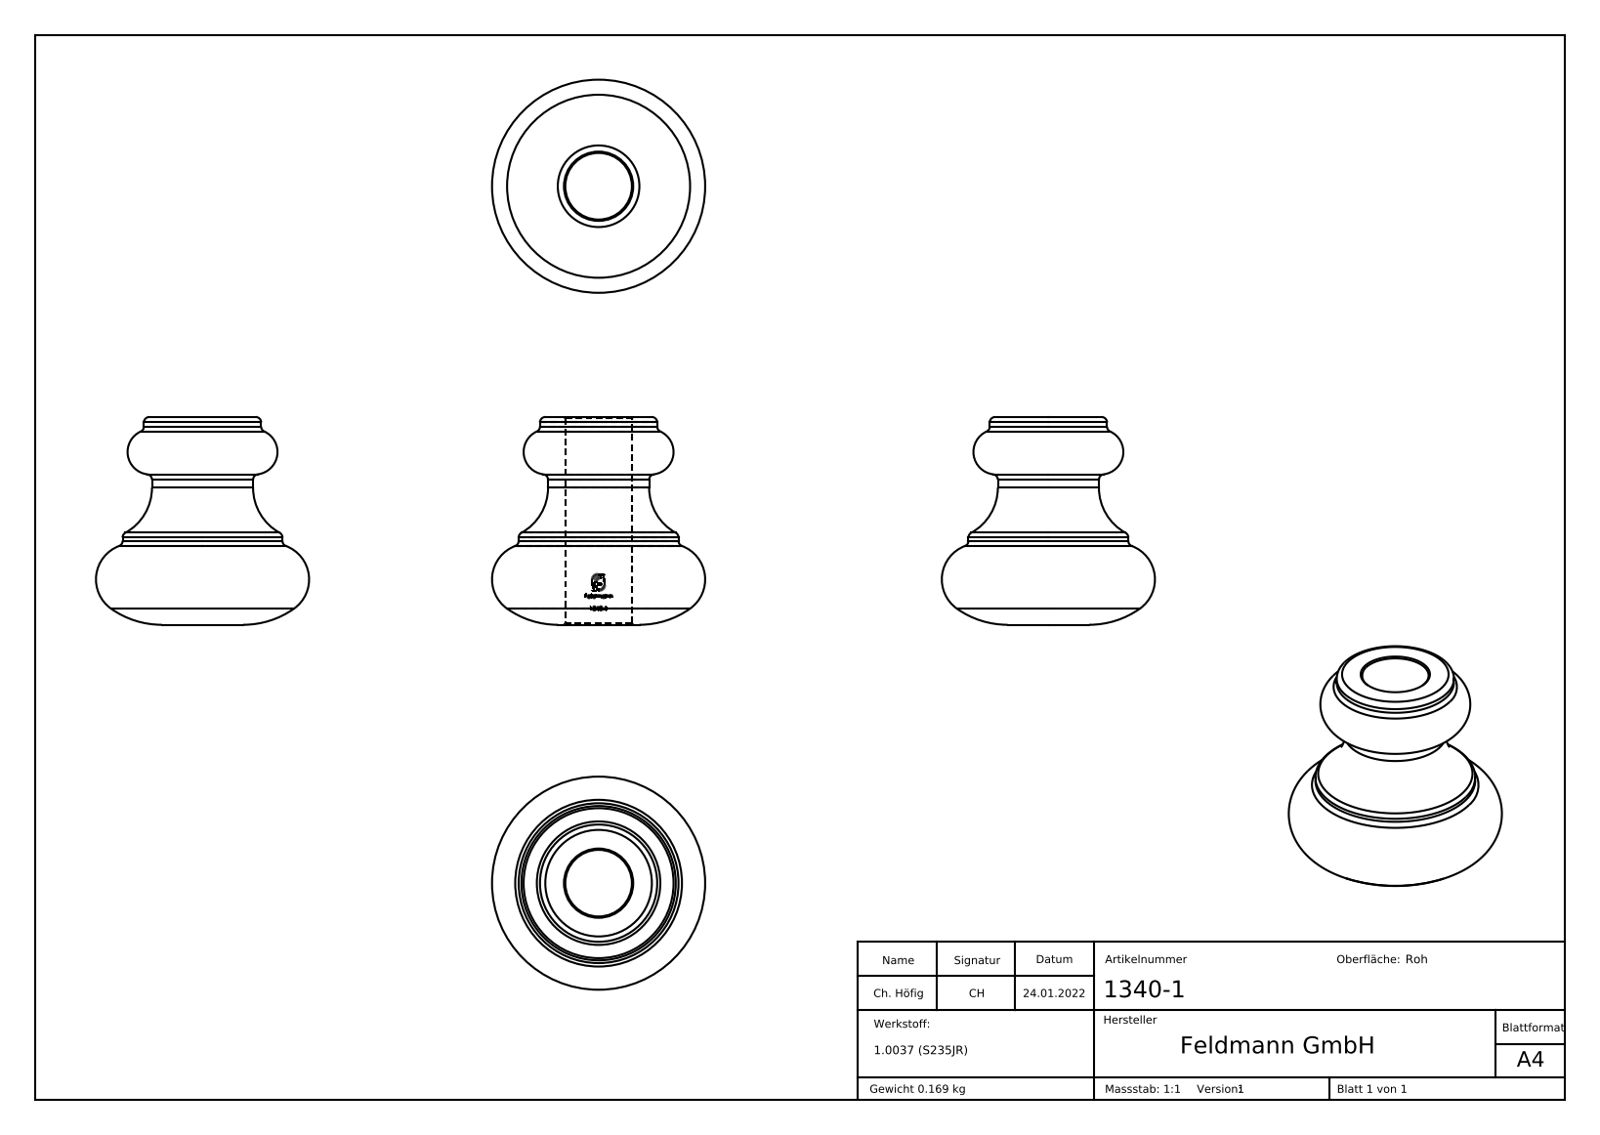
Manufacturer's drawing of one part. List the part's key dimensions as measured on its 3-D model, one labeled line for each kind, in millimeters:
Part name (STEP PRODUCT): 1340-1
STEP written by: SolidWorks 2018 (CONFIG_CONTROL_DESIGN)
Units: millimetres
Bodies: 1 solid, 251 faces (110 planar, 28 cylindrical, 113 other)
Overall size (bounding box): 40 × 40 × 39
Volume: 21 695 mm³ · Surface area: 6 608 mm²
Round holes (diameter × count): ⌀12.5 ×1
Round bosses / shafts (diameter × count): ⌀30 ×1, ⌀22 ×1, ⌀18.97 ×1
Partial cylindrical surfaces — rounded edges, fillets, slot ends (radius × count): R6.35 ×1
Main face-to-face distances: 39, 0.32, 2.45, 1.21, 1.28, 0.34, 2.2, 2.56, 1.14, 0.96
